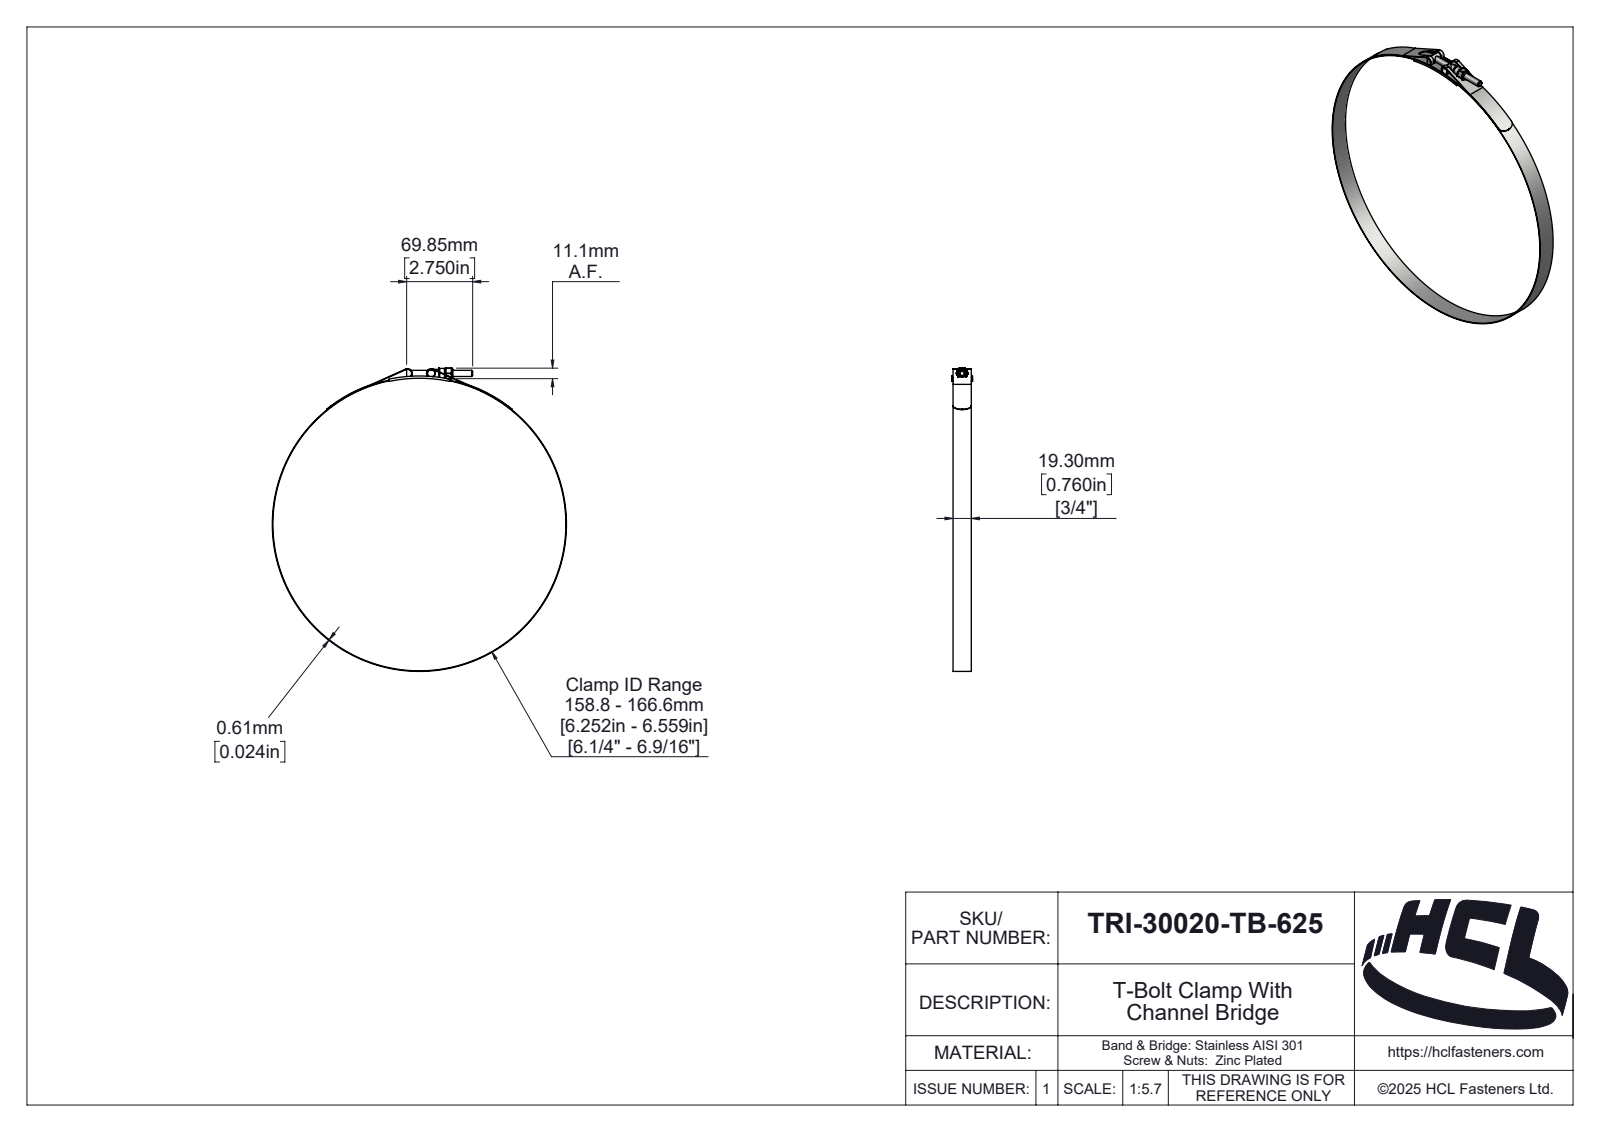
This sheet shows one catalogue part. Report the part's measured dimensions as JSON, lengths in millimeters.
{"part_name": "TRI-30020-TB-625", "step_written_by": "SolidWorks 2025 (AUTOMOTIVE_DESIGN)", "units": "millimeters", "bodies": {"solids": 6, "faces": 330, "planar": 44, "cylindrical": 122, "other": 164}, "overall_size": [320.84, 311.22, 22], "volume_mm3": 18516, "surface_area_mm2": 52986, "round_holes": [[5.4, 1], [6.35, 1], [6.5, 1], [7.58, 1], [310, 1]], "round_bosses_or_shafts": [[8.58, 2], [311.22, 1], [10.58, 1]], "partial_cylinders_radius": [[0.39, 6], [0.5, 2], [4.39, 2], [5, 2], [0.59, 1], [2.42, 1], [3.03, 1], [3.19, 1]], "face_to_face_distances": [0.61, 19.3, 1.35, 20.65, 0.74, 21.39, 20.04, 22, 20.78, 41], "hole_center_spacings": [160]}
